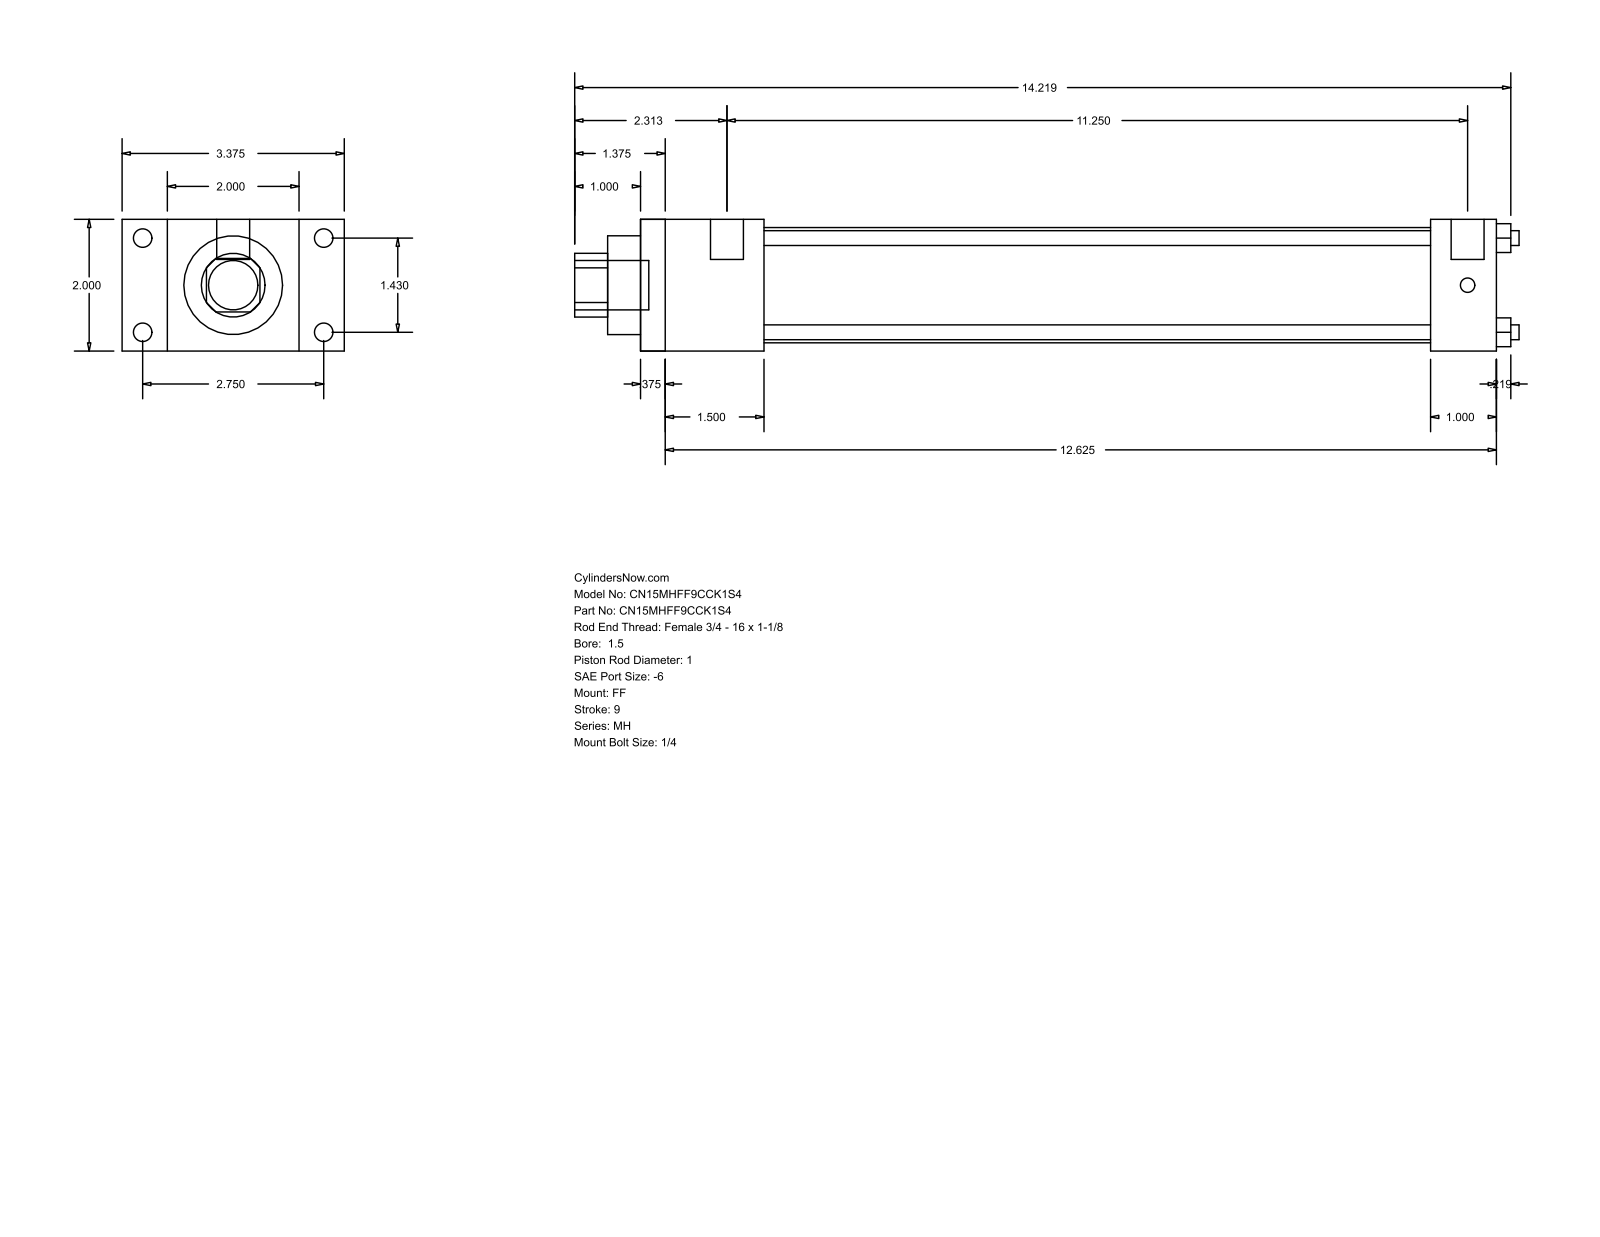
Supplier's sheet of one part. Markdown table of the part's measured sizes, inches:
| quantity | value |
| --- | --- |
| part name | MH_FF__0150_1 |
| STEP written by | GSSL Pune (CONFIG_CONTROL_DESIGN) |
| units | inches |
| bodies | 0 solids, 92 faces (64 planar, 28 cylindrical, 0 other) |
| overall size | 14.344 × 3.375 × 2 |
| round holes (diameter × count) | 0.225 × 4, 1 × 1, 1.5 × 1, 1.75 × 1 |
| round bosses / shafts (diameter × count) | 0.281 × 4, 0.219 × 4, 0.5 × 2, 0.75 × 1 |
| partial cylindrical surfaces (radius × count) | 0.484 × 1 |
| main face-to-face distances | 2, 13, 0.375, 12.625, 1, 0.687, 2.687, 1.875, 1.5, 11.125 |
| hole center spacings | 1.011, 1.43, 2.022 |
